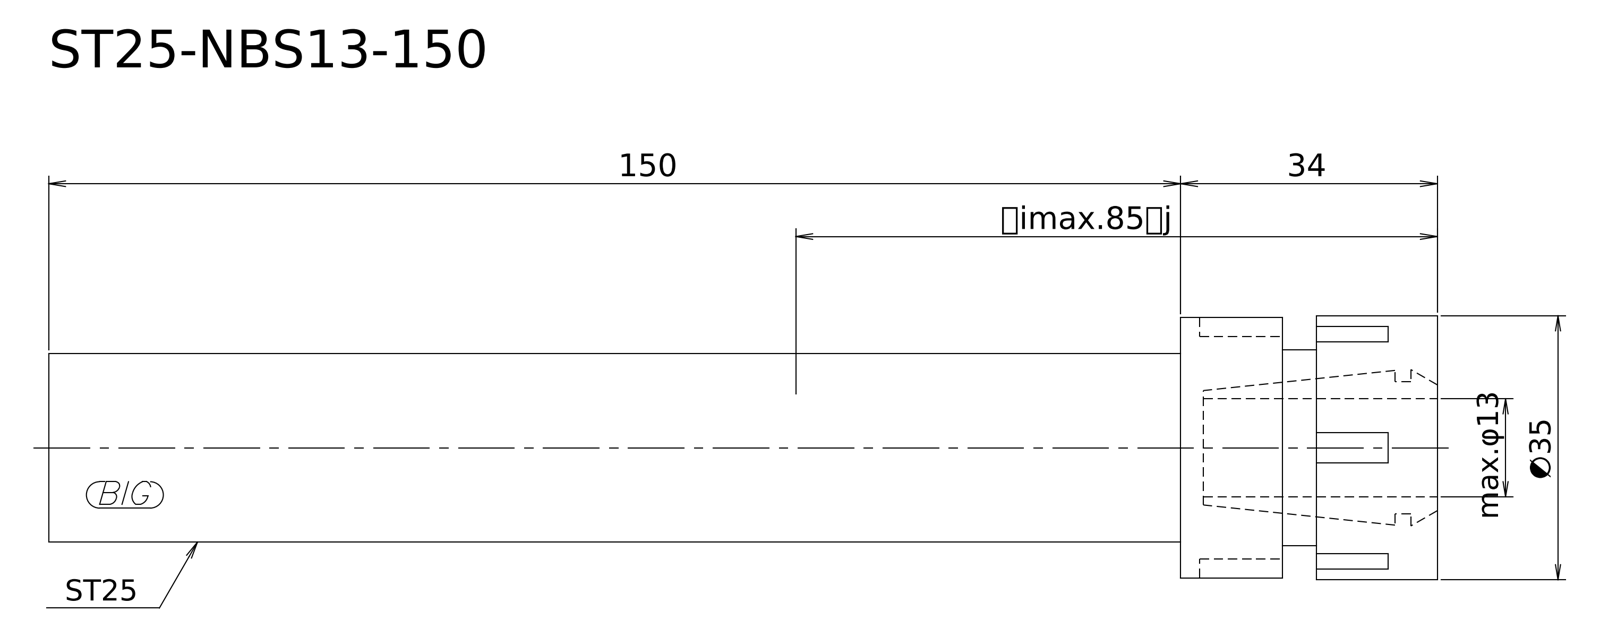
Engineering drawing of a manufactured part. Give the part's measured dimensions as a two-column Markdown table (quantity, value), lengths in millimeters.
| quantity | value |
| --- | --- |
| STEP written by | Kubotek KeyCreator V8.5.1 (14335) (CONFIG_CONTROL_DESIGN) |
| units | millimeters |
| bodies | 1 solid, 9 faces (5 planar, 4 cylindrical, 0 other) |
| overall size | 184 × 35 × 35 |
| volume | 104 034 mm³ |
| surface area | 18 103 mm² |
| round bosses / shafts (diameter × count) | 35 × 1, 34.5 × 1, 26 × 1, 25 × 1 |
| main face-to-face distances | 184, 34, 150, 16, 18, 168, 20.5, 4.5, 13.5, 163.5 |
